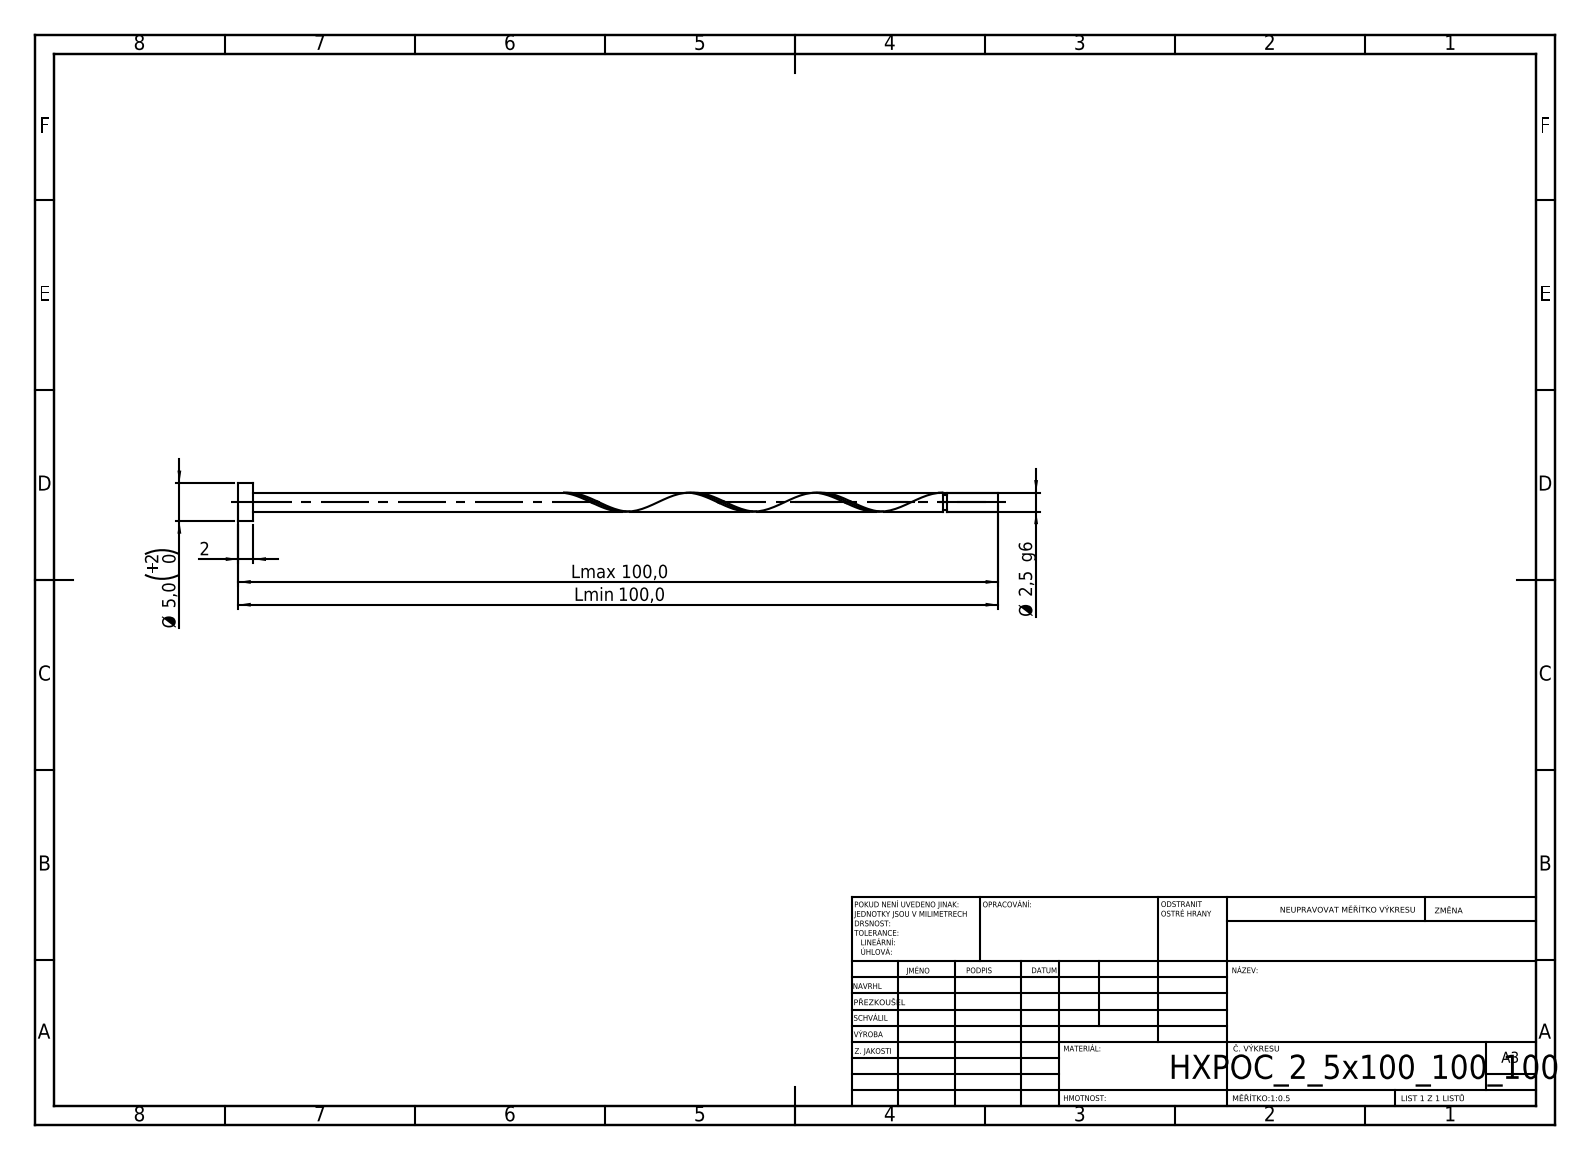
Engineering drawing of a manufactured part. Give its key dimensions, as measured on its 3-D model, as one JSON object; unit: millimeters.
{"step_written_by": "SolidWorks 2019 (CONFIG_CONTROL_DESIGN)", "units": "millimeters", "bodies": {"solids": 1, "faces": 21, "planar": 6, "cylindrical": 14, "other": 1}, "overall_size": [100, 5, 5], "volume_mm3": 515, "surface_area_mm2": 857, "round_bosses_or_shafts": [[5, 1], [2.5, 1], [2, 1]], "face_to_face_distances": [2, 100, 98, 93.25, 91.25, 6.75, 92.75, 90.75, 0.5, 7.25]}
